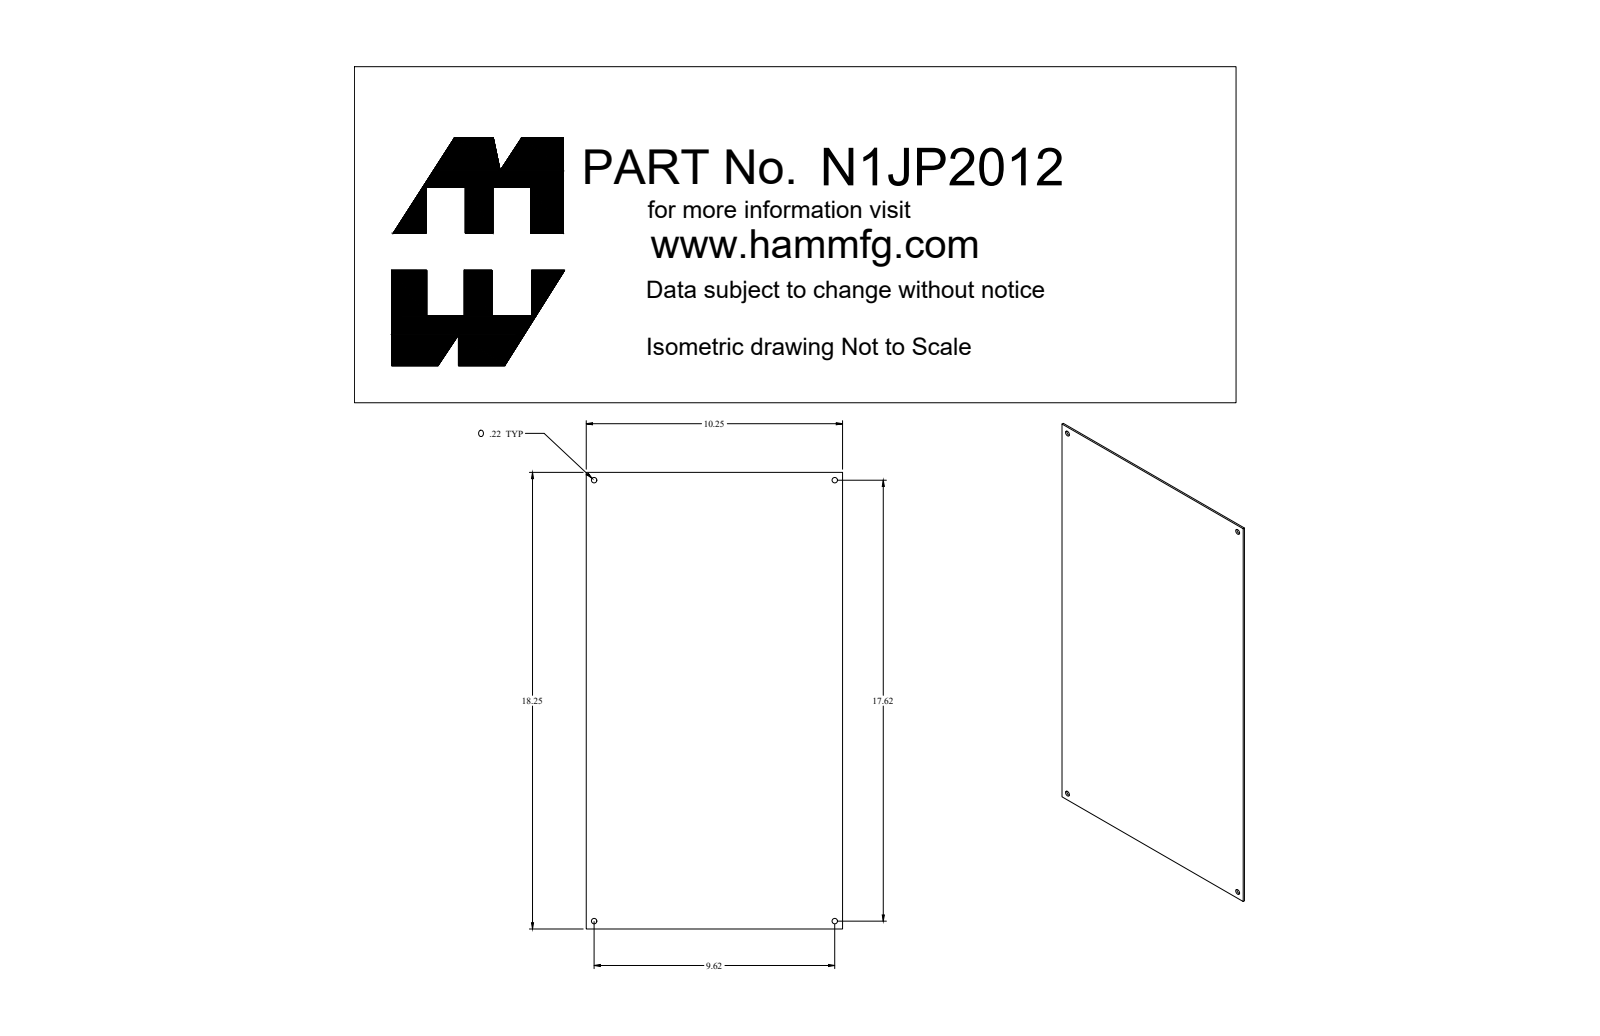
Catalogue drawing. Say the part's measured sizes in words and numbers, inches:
The part is named "N1JP2012". Its 3-D file was written by "SolidWorks 2018 (AUTOMOTIVE_DESIGN)". It is 1 solid with 18 faces: 6 planar, 12 cylindrical and 0 other. Overall it measures 18.25 by 10.25 by 0.072 inches. Its volume is 13.45 cubic inches and its surface area 378 square inches. Round holes: 4 of diameter 0.265. Partial cylindrical surfaces (rounded edges, fillets, slot ends): 4 of radius 0.125. The main face-to-face distances are 0.072, 10.25, 18.25. The hole center spacings are 9.625, 17.625, 20.081.
